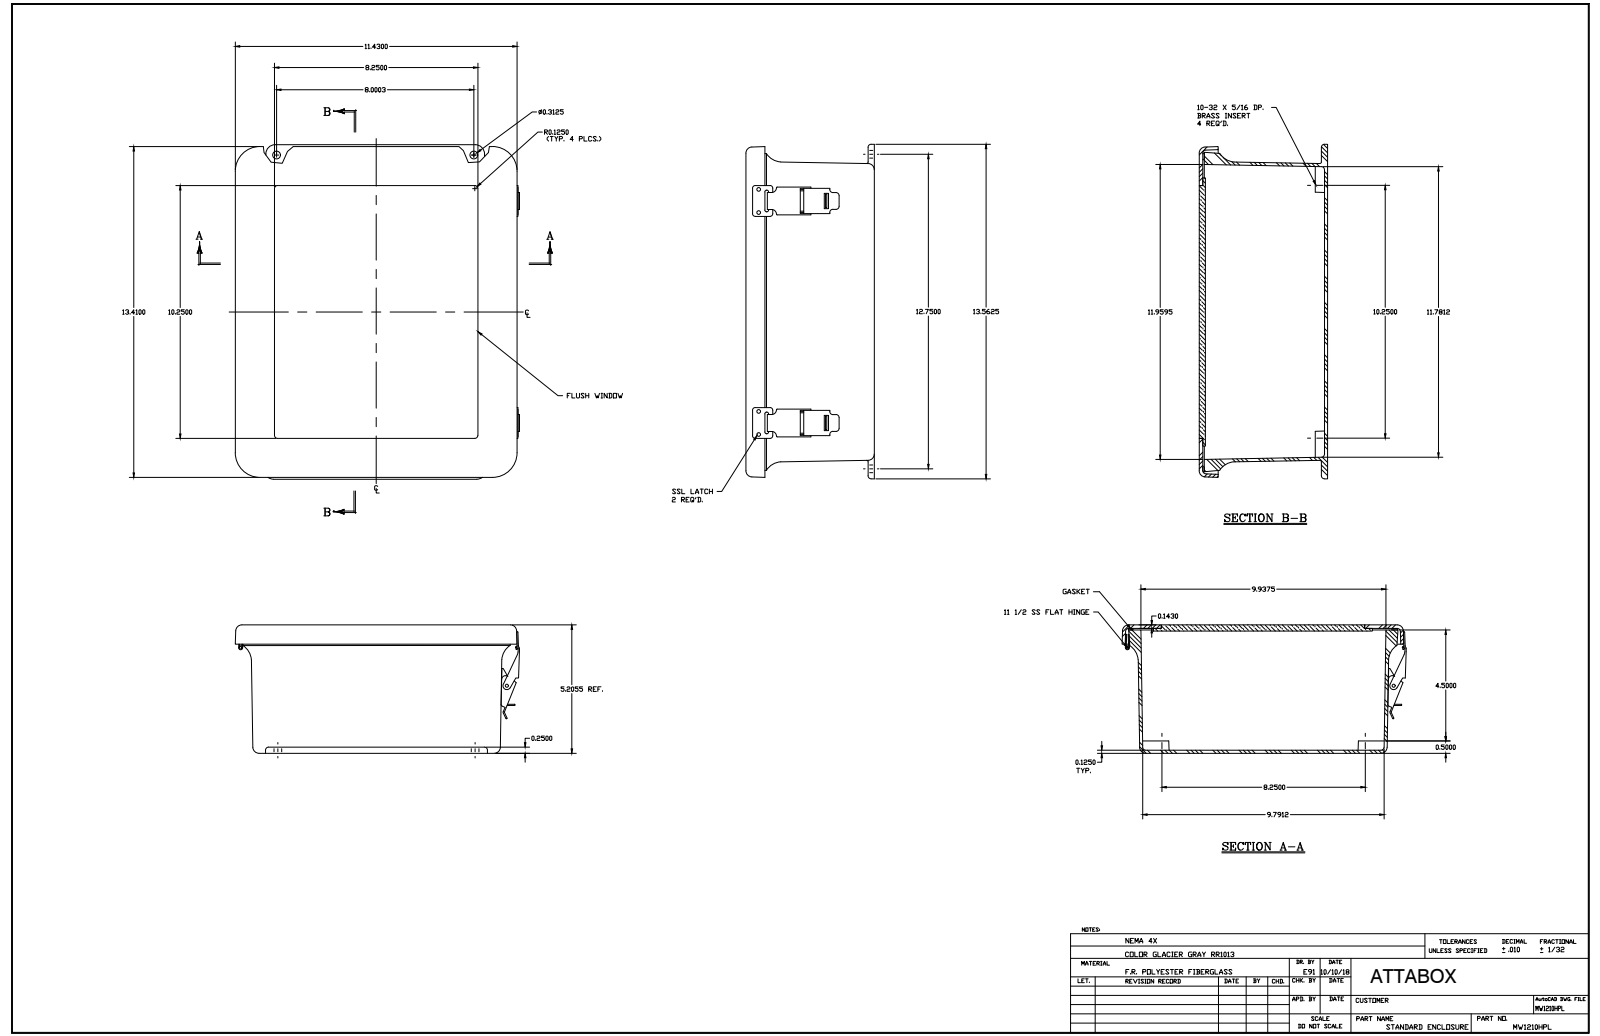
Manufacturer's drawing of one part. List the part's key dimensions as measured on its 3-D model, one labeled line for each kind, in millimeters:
Part name (STEP PRODUCT): MW1210HPL
STEP written by: SolidWorks 2018 (AUTOMOTIVE_DESIGN)
Units: millimetres
Bodies: 39 solids, 1006 faces (438 planar, 421 cylindrical, 147 other)
Overall size (bounding box): 344.5 × 293.3 × 132.6
Volume: 1 600 000 mm³ · Surface area: 798 100 mm²
Round holes (diameter × count): ⌀3.6 ×20, ⌀2.6 ×8, ⌀3.3 ×8, ⌀3.9 ×5, ⌀3.3 ×4, ⌀4 ×4, ⌀5.5 ×4, ⌀3.4 ×2, ⌀9.5 ×2, ⌀2.2 ×1, ⌀2.2 ×1, ⌀3.4 ×1
Round bosses / shafts (diameter × count): ⌀3.2 ×12, ⌀6.4 ×8, ⌀6.9 ×4, ⌀3.2 ×4, ⌀7.6 ×1, ⌀4.3 ×1, ⌀3.9 ×1, ⌀3 ×1
Partial cylindrical surfaces — rounded edges, fillets, slot ends (radius × count): R3.2 ×24, R0.4 ×20, R0.8 ×20, R1.1 ×16, R0.8 ×12, R6.4 ×12, R0.6 ×9, R1.5 ×6
Main face-to-face distances: 132.6, 3.2, 6.4, 129.4, 126.2, 123, 128.9, 125.8, 2.7, 3.6
Hole centre spacings: 228.6, 23.8, 19.1, 92.1, 229.4, 6.4, 34.2, 36.9
